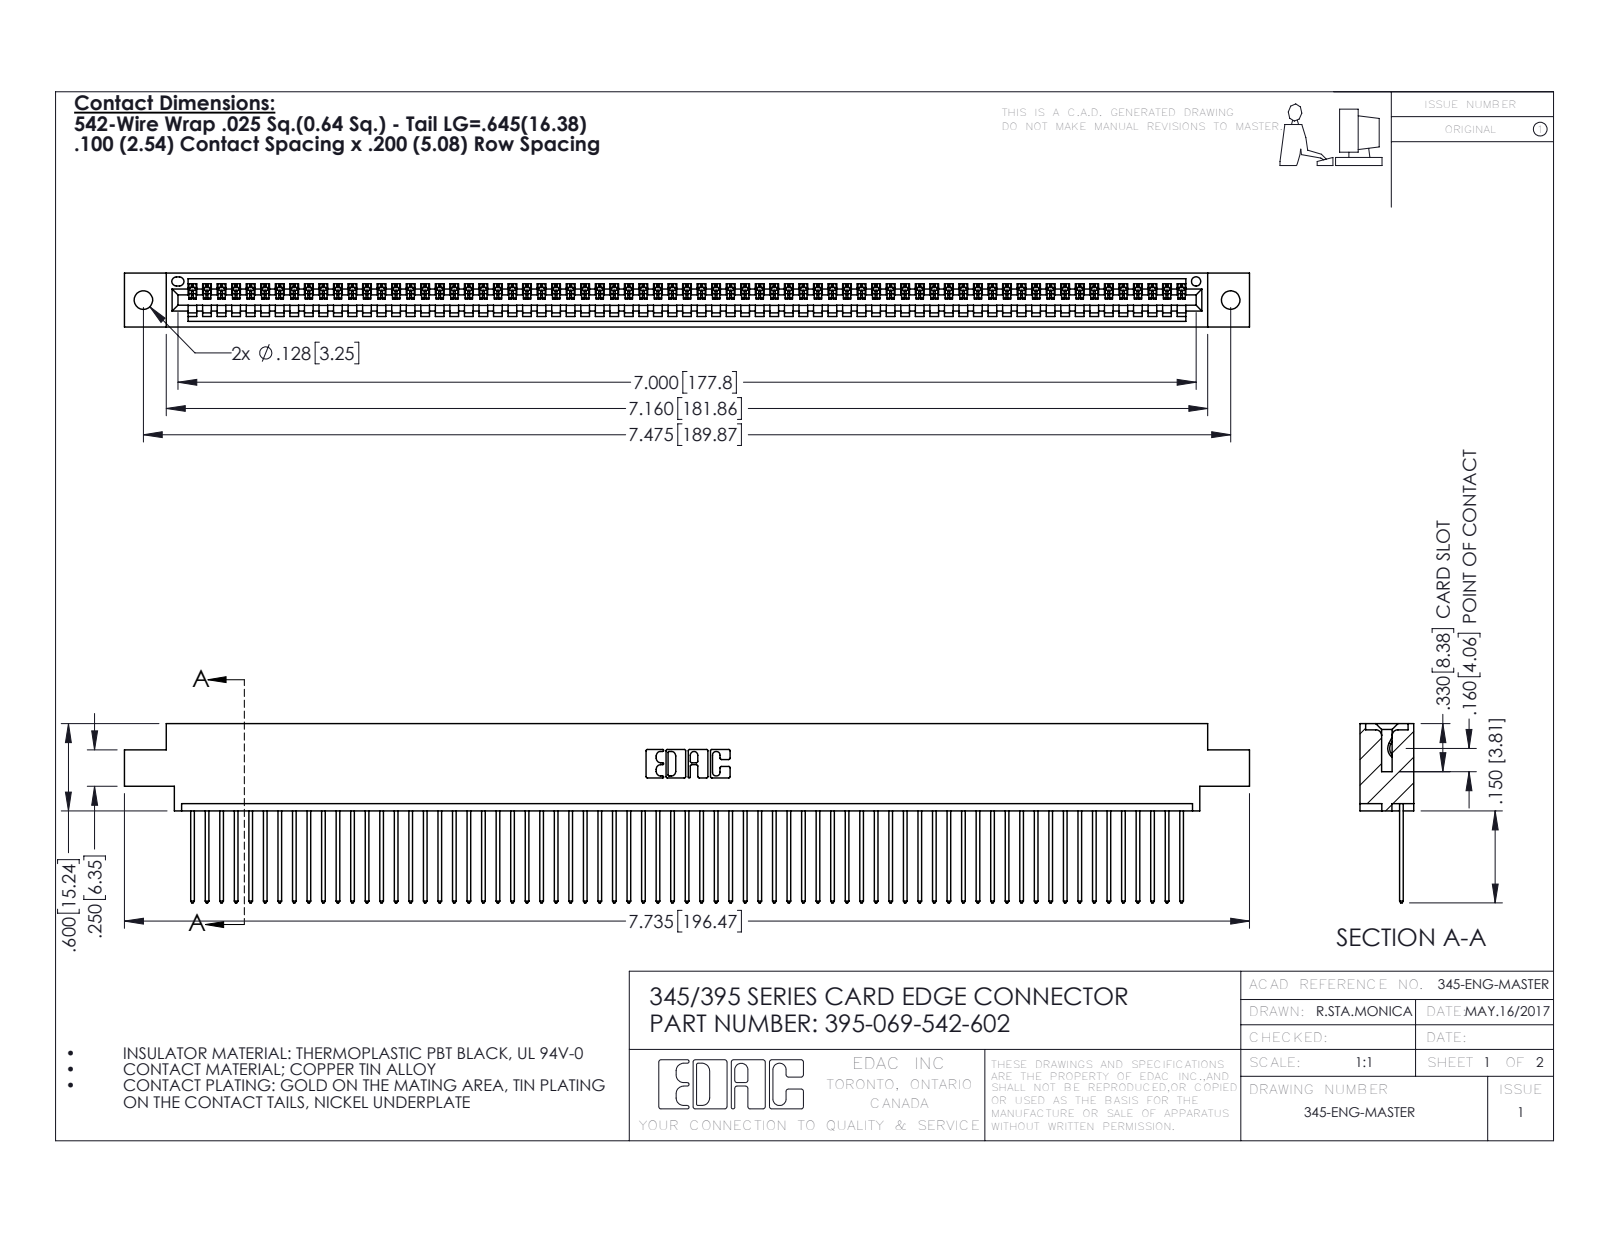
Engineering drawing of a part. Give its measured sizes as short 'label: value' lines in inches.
name: 345 Part_0.170 Offset - 0.128 Dia; 345-292-001_345-293-142; 395-069-542-602
written by: SolidWorks 2016 (CONFIG_CONTROL_DESIGN)
unit: in
bodies: 70 solids, 4132 faces (2844 planar, 1288 cylindrical, 0 other)
size: 7.735 × 1.232 × 0.37
volume: 1.152 in³; area: 40.75 in²
holes: 2× ⌀0.128, 1× ⌀0.064
rounds: 138× R0.006, 138× R0.01, 22× R0.01, 6× R0.007, 6× R0.031, 3× R0.026, 2× R0.031, 2× R0.04
face distances: 0.072, 0.298, 0.37, 0.098, 0.272, 0.025, 0.2, 0.225, 0.175, 0.149
hole spacings: 0.27, 7.239, 7.475
